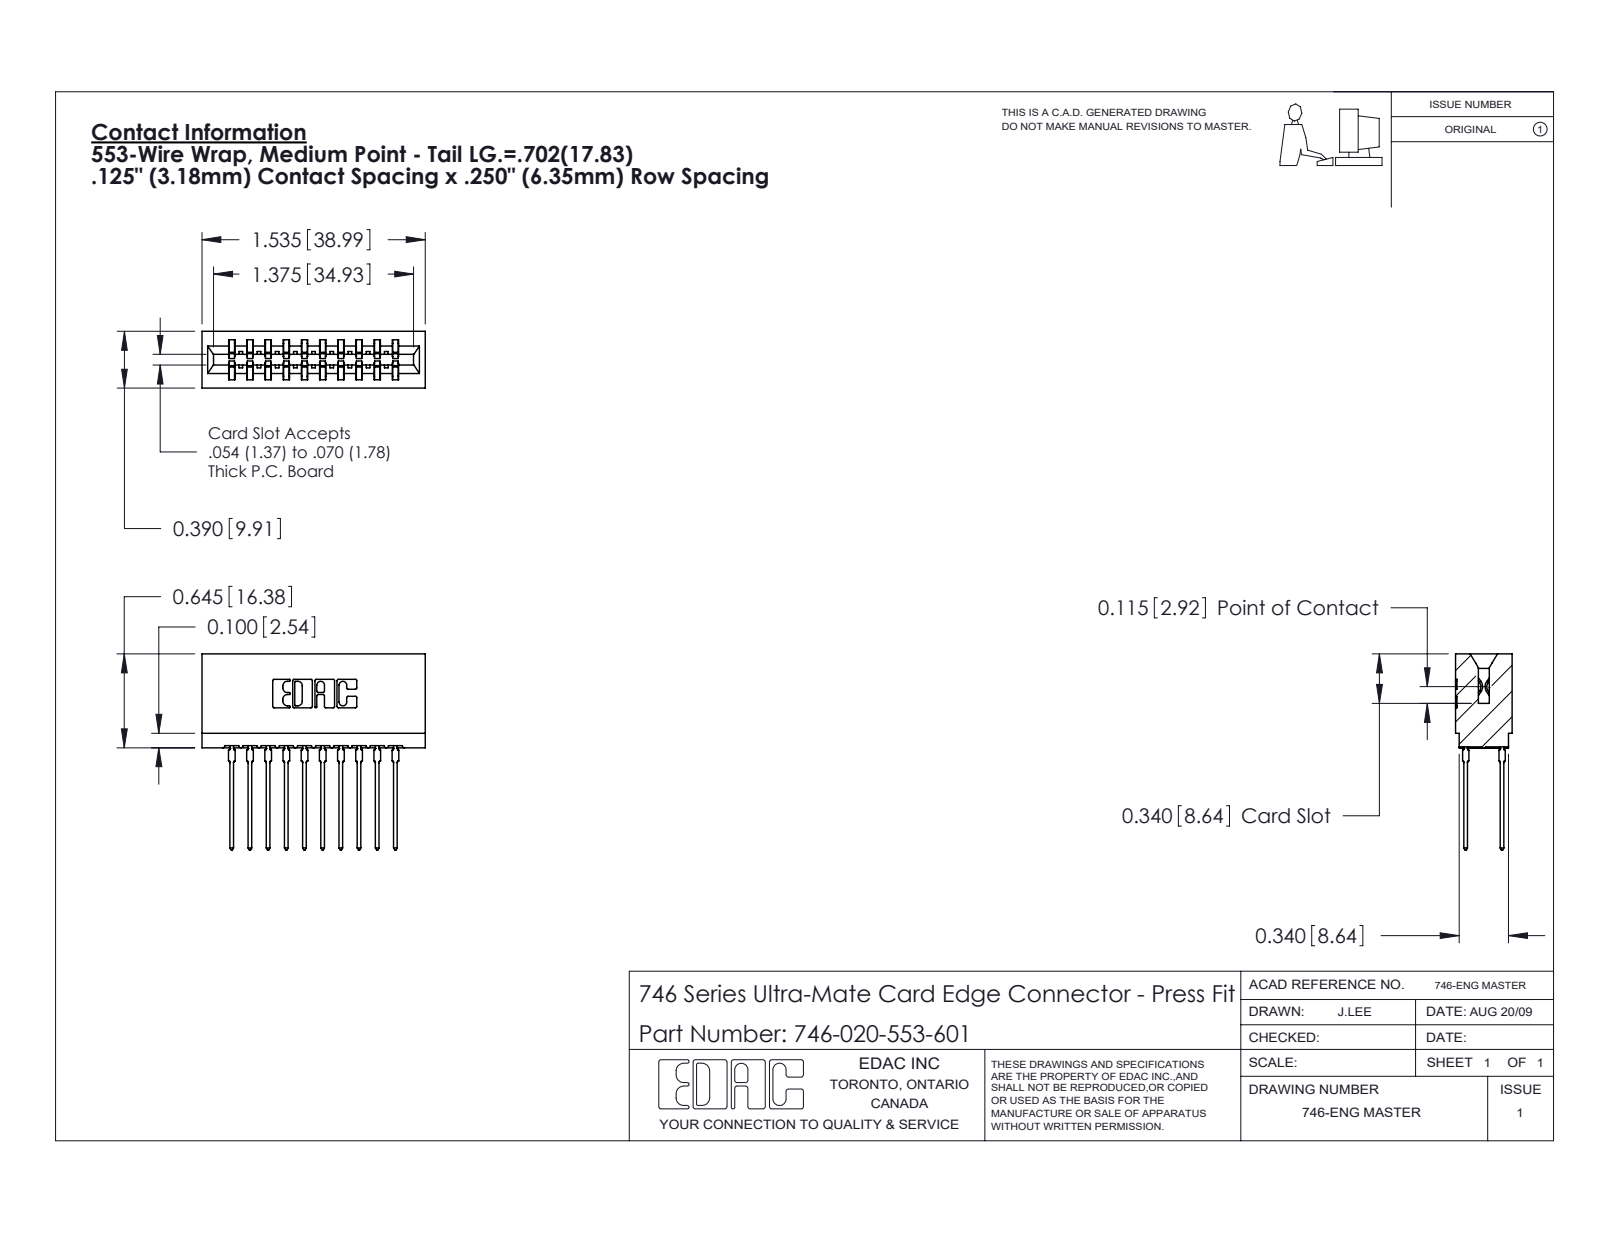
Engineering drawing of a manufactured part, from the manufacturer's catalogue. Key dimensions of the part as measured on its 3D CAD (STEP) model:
Part name (STEP PRODUCT): 746-292-001_553; 746 Part_.340 Slot Depth - 01; 746-020-553-601
STEP written by: SolidWorks 2020 (CONFIG_CONTROL_DESIGN)
Units: inches
Bodies: 21 solids, 1887 faces (975 planar, 392 cylindrical, 520 other)
Overall size (bounding box): 1.535 × 1.346 × 0.39
Volume: 0.29 in³ · Surface area: 10.54 in²
Partial cylindrical surfaces — rounded edges, fillets, slot ends (radius × count): R0.021 ×40, R0.01 ×22, R0.015 ×11, R0.005 ×8, R0.011 ×8, R0.007 ×6, R0.031 ×6, R0.026 ×3
Main face-to-face distances: 0.25, 0.057, 0.333, 0.5, 0.042, 0.125, 0.083, 0.292, 0.375, 0.125
